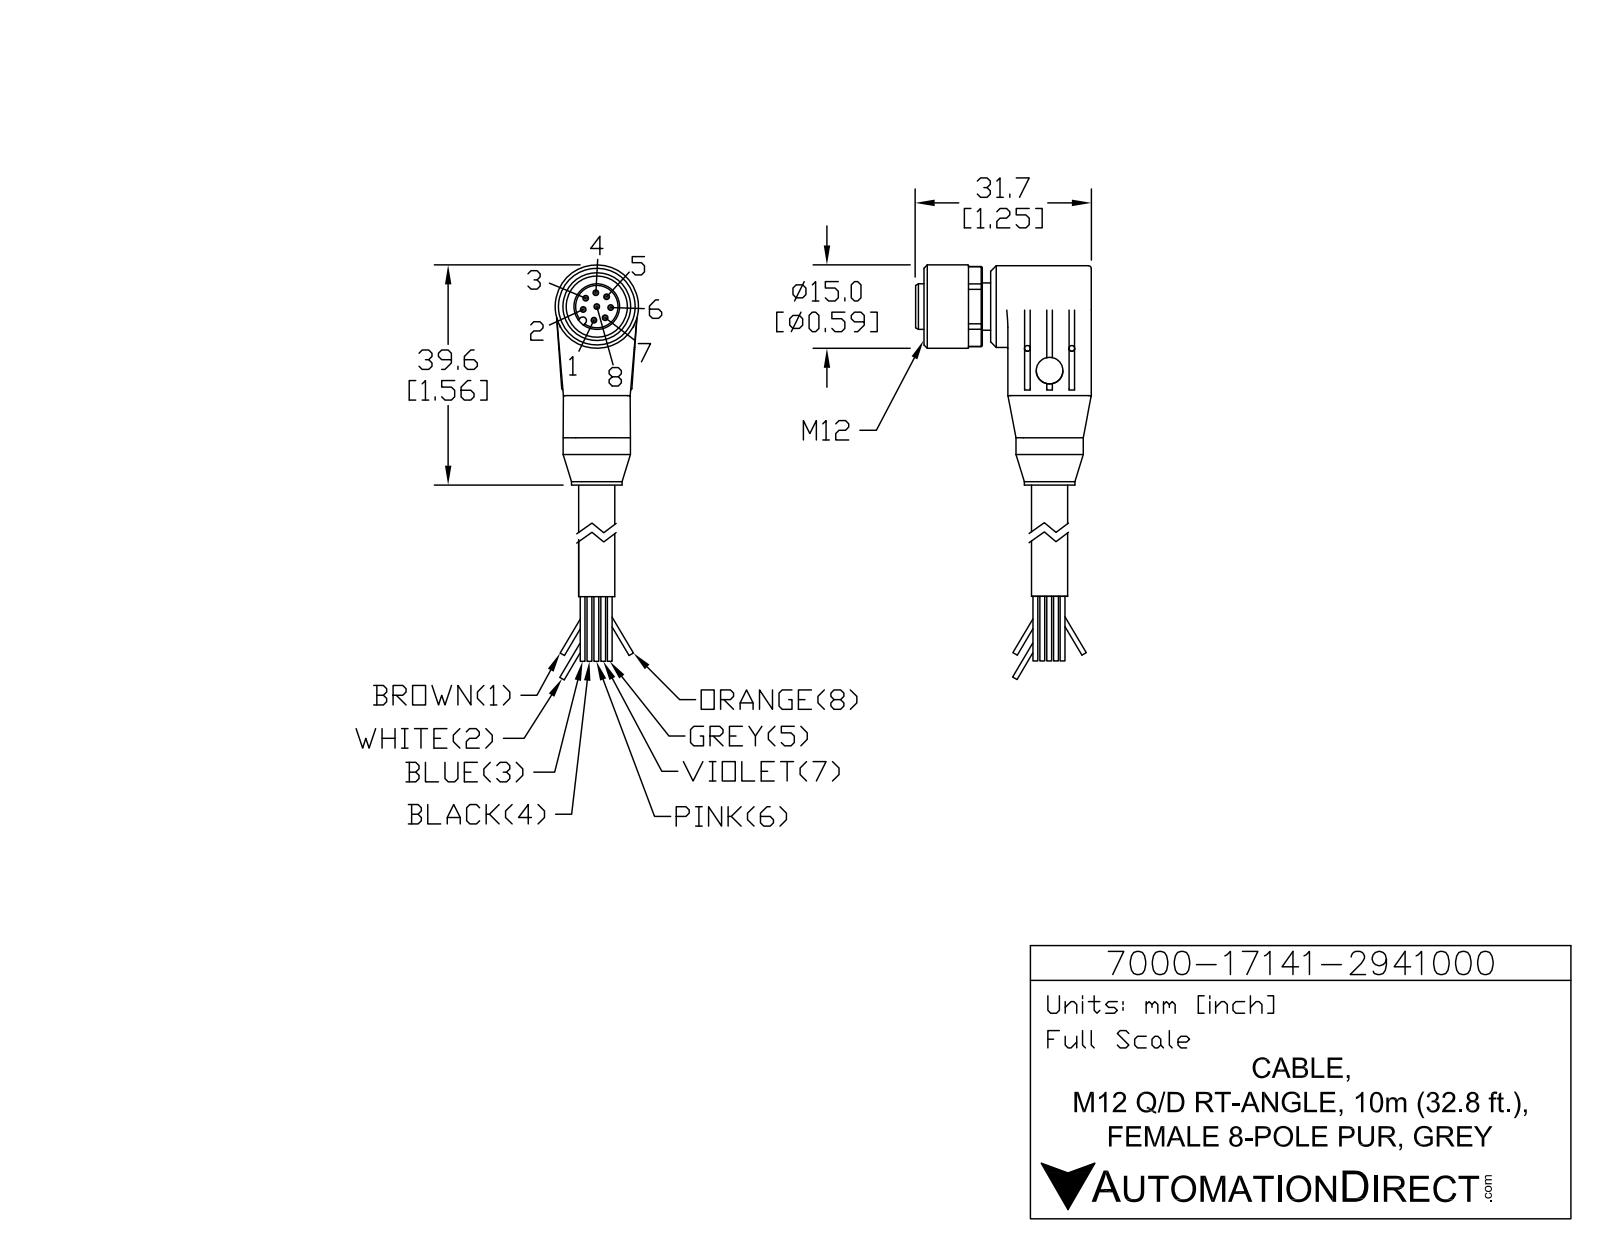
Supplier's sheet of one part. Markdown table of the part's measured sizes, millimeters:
| quantity | value |
| --- | --- |
| part name | 7000-17141-2941000 |
| STEP written by | SolidWorks 2015 (AUTOMOTIVE_DESIGN) |
| units | millimeters |
| bodies | 1 solid, 174 faces (73 planar, 67 cylindrical, 34 other) |
| overall size | 59.6 × 31.7 × 15 |
| volume | 9 094 mm³ |
| surface area | 4 084 mm² |
| round holes (diameter × count) | 1 × 8, 1.05 × 4, 4.8 × 1, 11 × 1 |
| round bosses / shafts (diameter × count) | 15 × 1, 14.7 × 1, 12.1 × 1, 9.1 × 1, 8.5 × 1, 8.2 × 1, 6.5 × 1 |
| partial cylindrical surfaces (radius × count) | 0.5 × 4, 0.3 × 2, 0.65 × 1, 7.2 × 1 |
| main face-to-face distances | 2.5, 15, 4.7, 17.5, 19.7, 2.2, 3, 7.7, 12, 16.7 |
| hole center spacings | 2.5, 2.07, 3.78, 4.95, 2.08, 4.22, 4.79, 4.8 |
